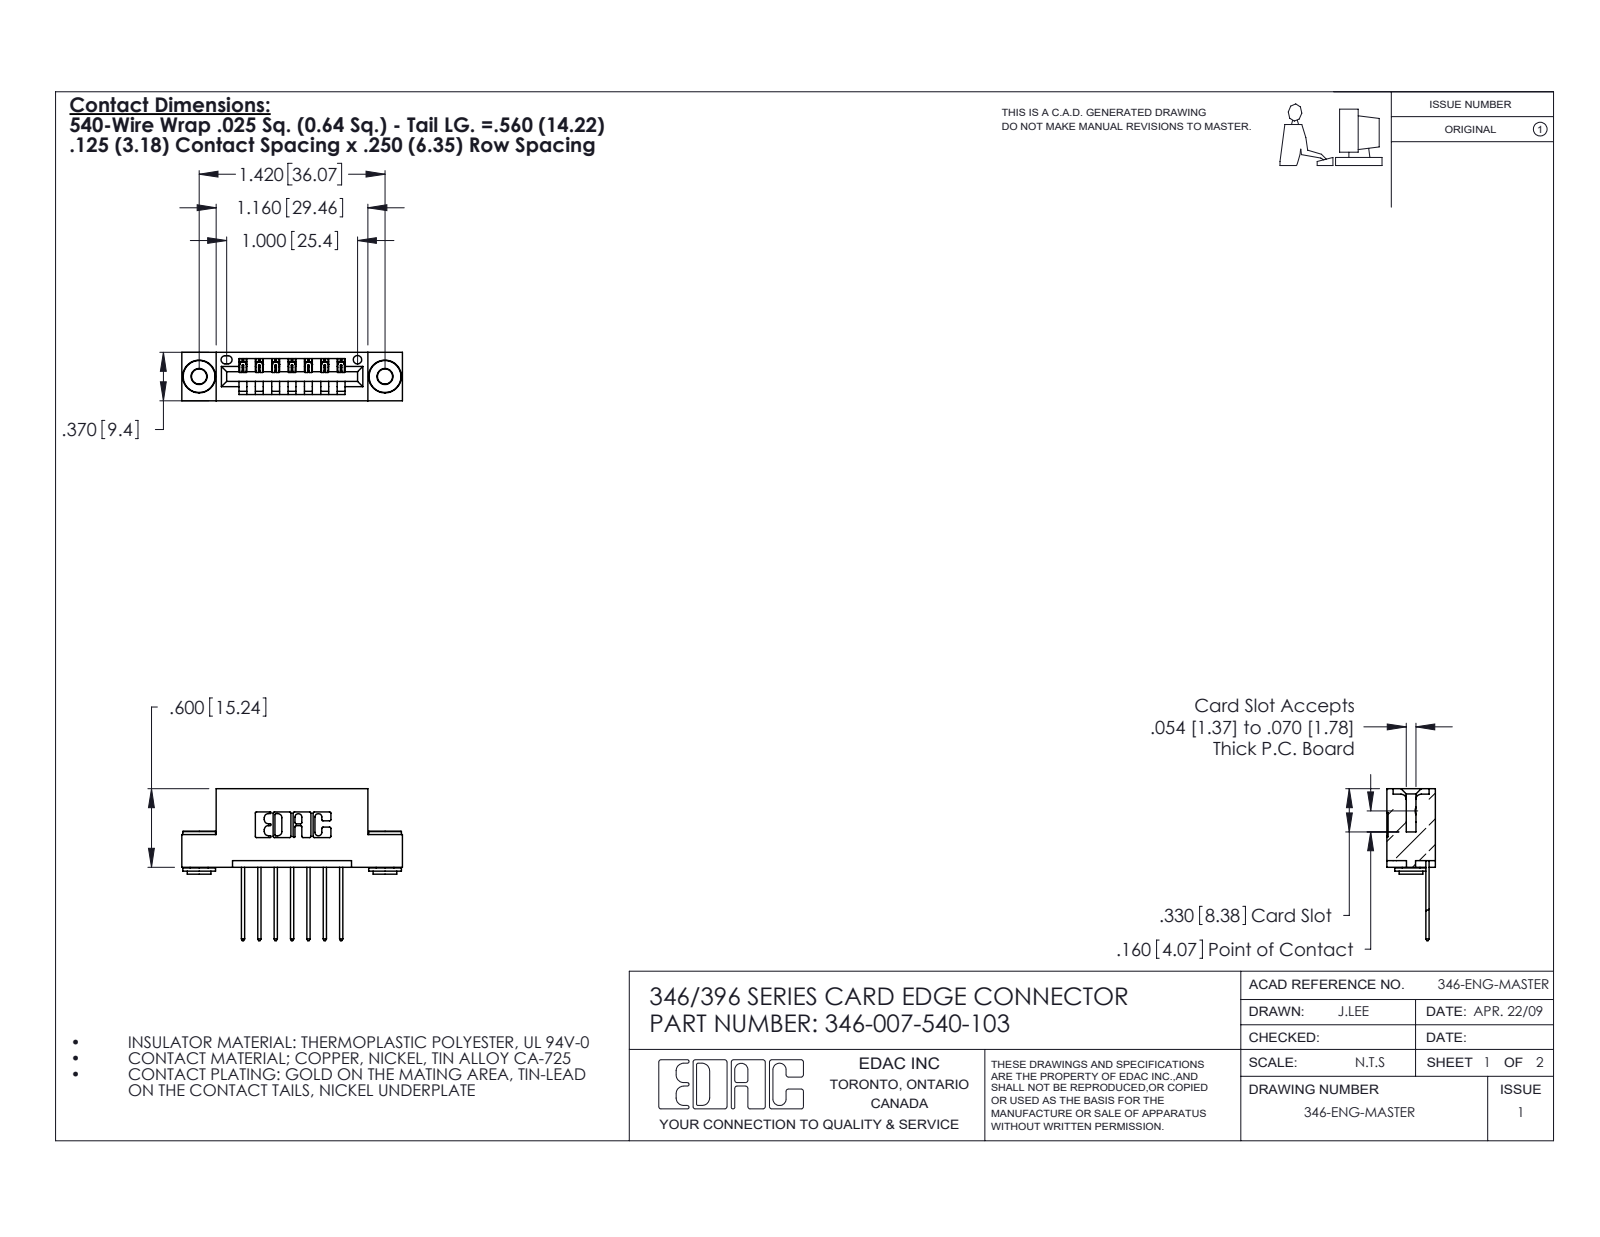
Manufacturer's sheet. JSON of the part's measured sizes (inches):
{"part_name": "345-250-002_345-250-002-102; 345-292-001_345-293-140; 346 Part_Flush Mounting Lugs - 0.156 Dia-TH; 346-007-540-103", "step_written_by": "SolidWorks 2020 (CONFIG_CONTROL_DESIGN)", "units": "inches", "bodies": {"solids": 10, "faces": 580, "planar": 380, "cylindrical": 192, "other": 8}, "overall_size": [1.685, 1.16, 0.37], "volume_in3": 0.236, "surface_area_in2": 7.402, "round_holes": [[0.116, 2], [0.156, 2], [0.064, 1]], "round_bosses_or_shafts": [[0.25, 2], [0.18, 2], [0.136, 2]], "partial_cylinders_radius": [[0.01, 22], [0.006, 14], [0.01, 14], [0.007, 6], [0.031, 6], [0.026, 3], [0.031, 2], [0.04, 2]], "face_to_face_distances": [0.25, 0.37, 0.048, 0.322, 0.025, 0.072, 0.298, 0.148, 0.222, 0.1], "hole_center_spacings": [0.246, 1.217, 1.42]}
